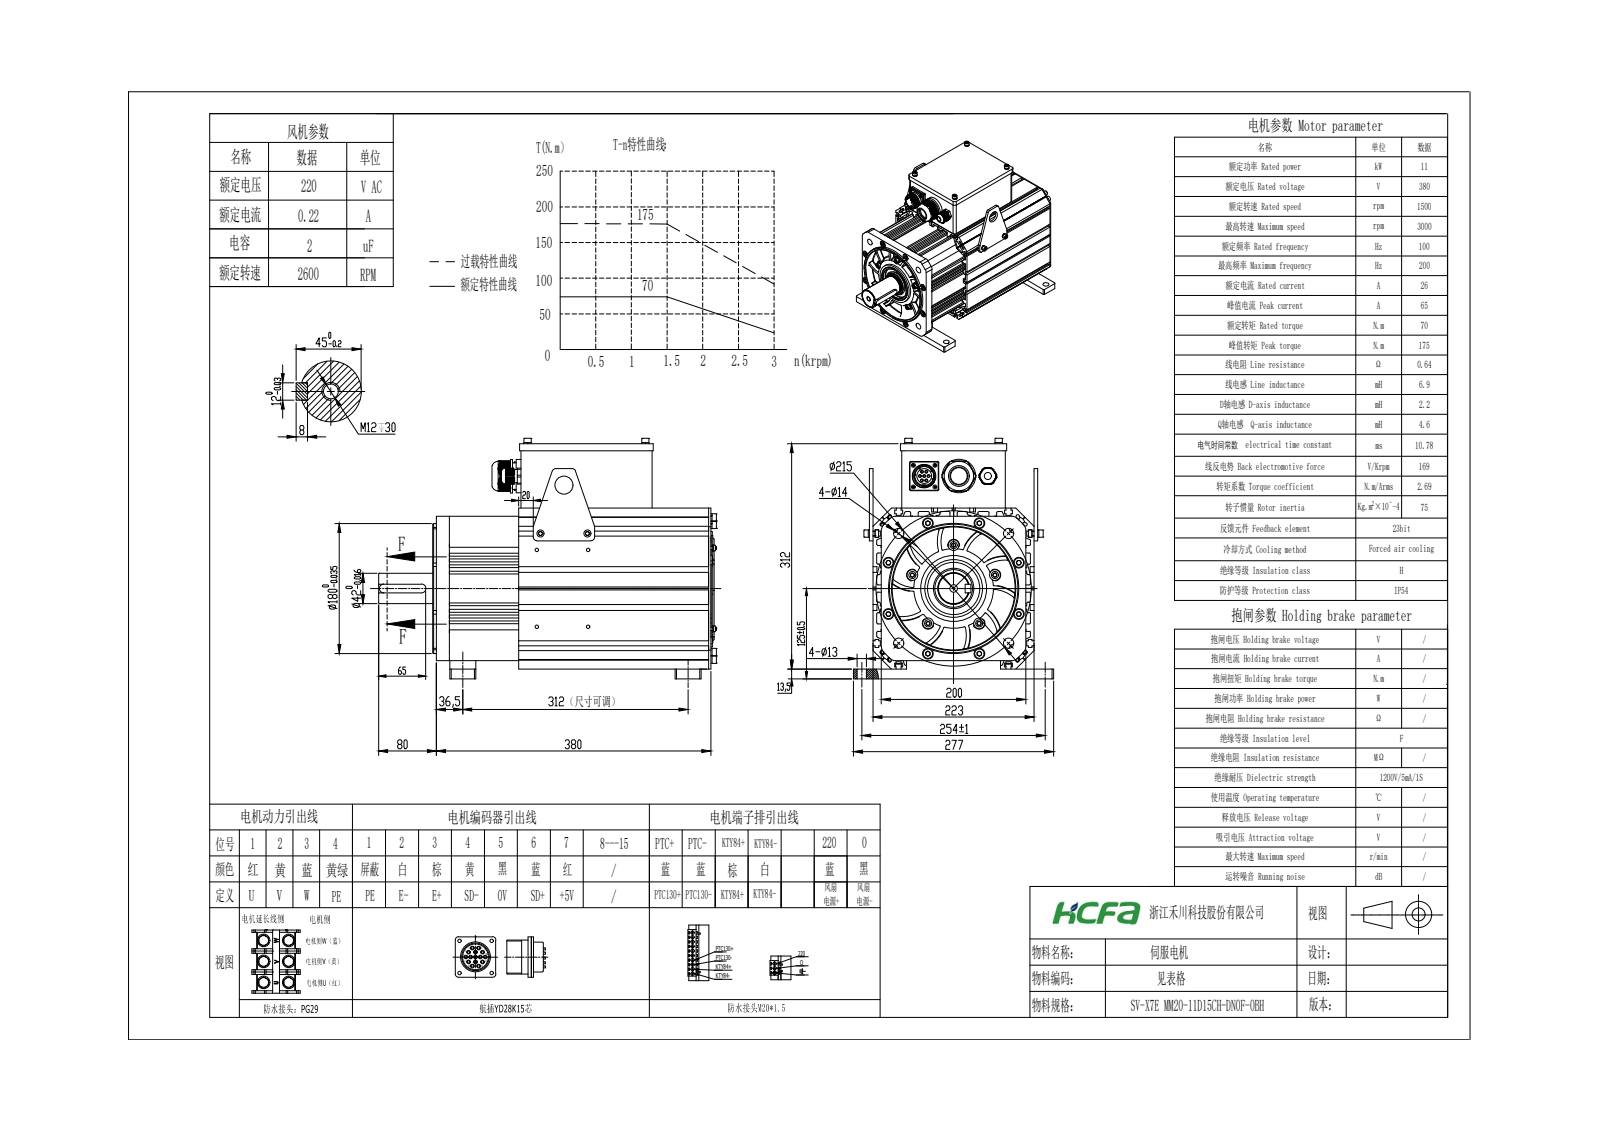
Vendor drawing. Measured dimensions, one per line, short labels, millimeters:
name: 11KW
written by: SolidWorks 2021 (CONFIG_CONTROL_DESIGN)
unit: mm
bodies: 111 solids, 4173 faces (2310 planar, 1117 cylindrical, 746 other)
size: 467.6 × 333.1 × 277
volume: 5 371 000 mm³; area: 1 996 000 mm²
holes: 19× ⌀2.5, 19× ⌀6.5, 19× ⌀6.68, 16× ⌀4.2, 14× ⌀9, 10× ⌀15, 8× ⌀6.8, 6× ⌀4.5, 5× ⌀14, 4× ⌀3.2, 4× ⌀3.4, 4× ⌀4.4
bosses: 24× ⌀2, 19× ⌀10, 19× ⌀9.88, 19× ⌀6, 19× ⌀3, 15× ⌀3.5, 12× ⌀8, 8× ⌀13
rounds: 89× R2, 16× R5, 8× R1.5, 8× R2.41, 8× R2.5, 8× R3, 8× R10, 5× R7.5
face distances: 223, 2.5, 5, 11.5, 6.5, 211.5, 218, 206.5, 13, 210
hole spacings: 71, 25.45, 39.3, 42.89, 50.36, 52.92, 63.06, 97
